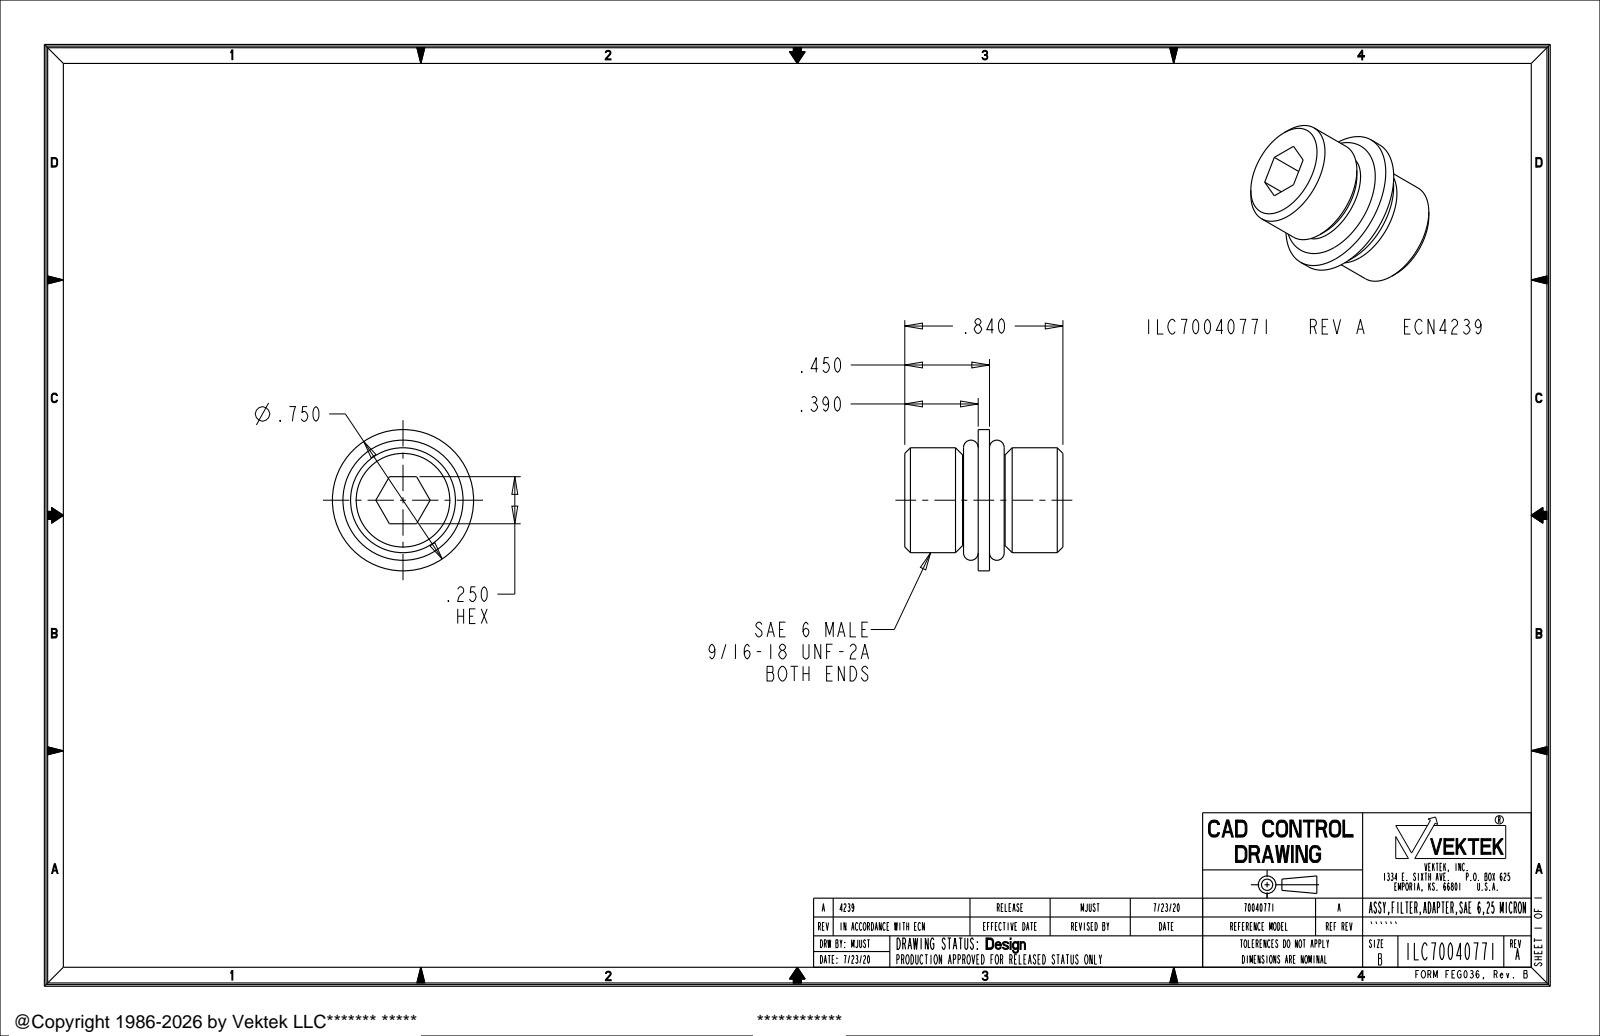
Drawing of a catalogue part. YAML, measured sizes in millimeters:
part_name: "ILC70040771"
step_written_by: "PRO/ENGINEER BY PARAMETRIC TECHNOLOGY CORPORATION, 2017170 (AUTOMOTIVE_DESIGN)"
units: millimeters
bodies: {solids: 3, faces: 44, planar: 12, cylindrical: 12, other: 20}
overall_size: [21.3, 19.1, 19.1]
volume: 2900
surface_area: 2510
round_holes:
  - {diameter: 10, count: 1}
round_bosses_or_shafts:
  - {diameter: 19.1, count: 1}
  - {diameter: 14.1, count: 1}
  - {diameter: 12.2, count: 1}
face_to_face_distances: [6.4, 1.5, 9.9, 11.4, 7.1, 8.6, 18.5, 2.8, 21.3, 7.6]
